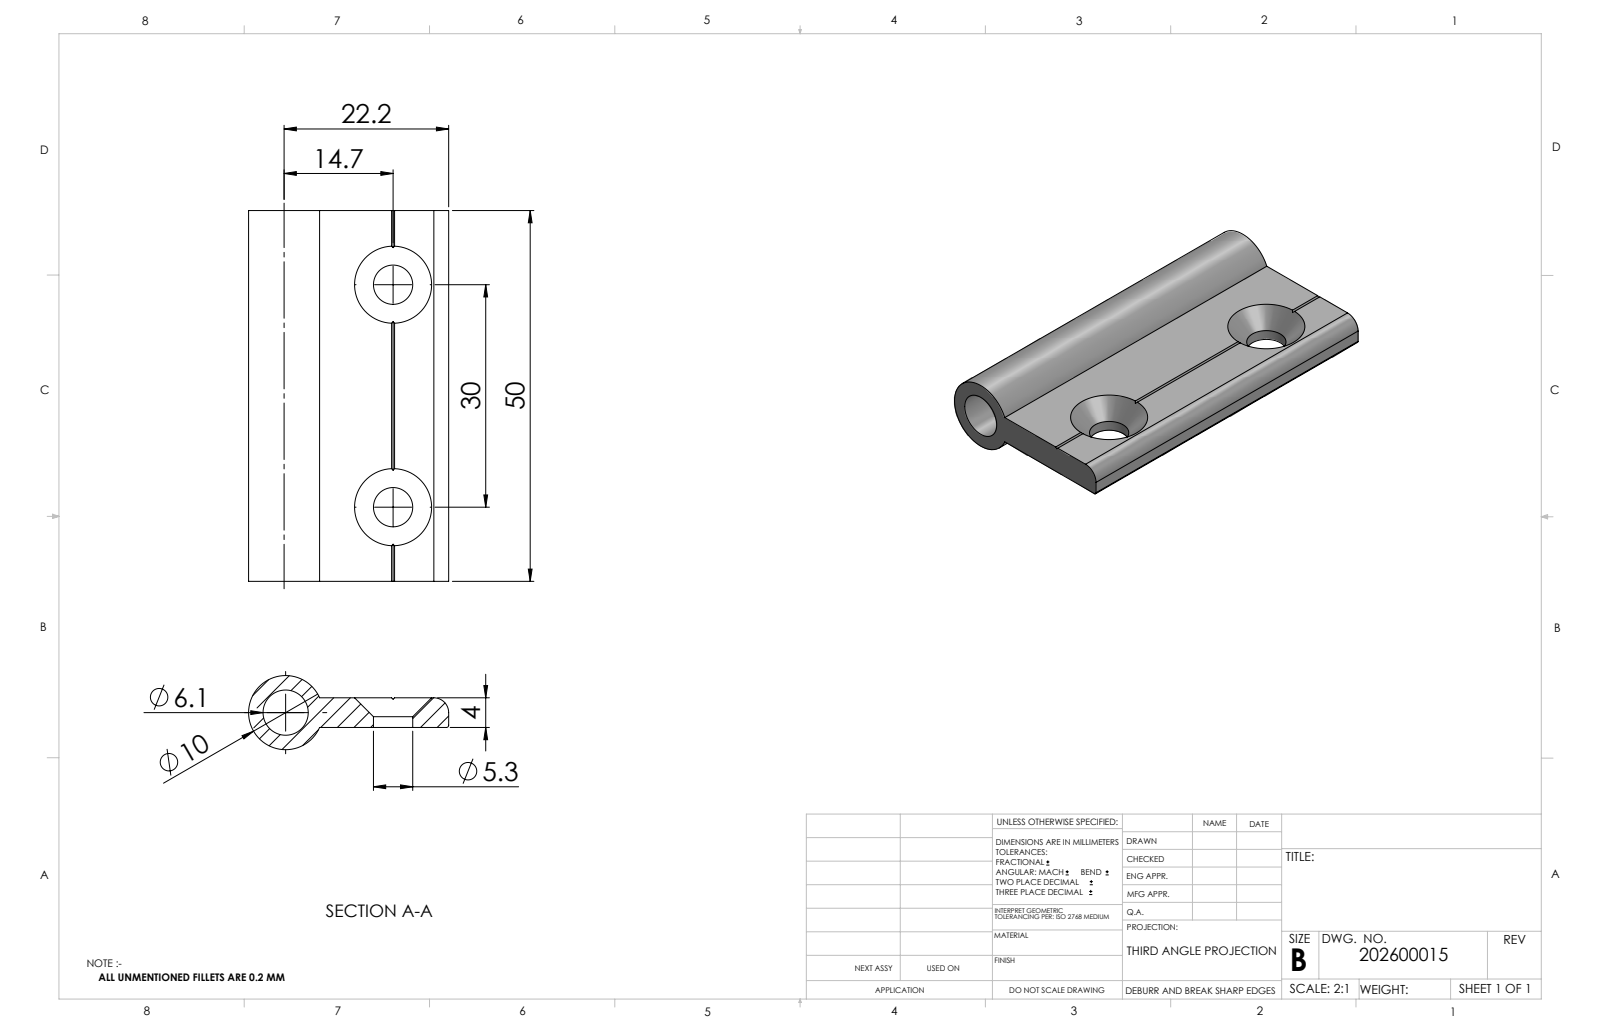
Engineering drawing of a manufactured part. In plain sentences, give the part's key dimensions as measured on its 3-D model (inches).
The part is named "202600015_c_1". Its 3-D file was written by "SolidWorks 2014 (CONFIG_CONTROL_DESIGN)". It is 1 solid with 26 faces: 12 planar, 10 cylindrical and 4 other. Overall it measures 1.969 by 1.063 by 0.394 inches. Its volume is 0.337 cubic inches and its surface area 6.922 square inches. Round holes: 2 of diameter 0.209, 1 of diameter 0.24. Round bosses or shafts: 1 of diameter 0.394. Partial cylindrical surfaces (rounded edges, fillets, slot ends): 1 of radius 0.012, 1 of radius 0.079. The main face-to-face distances are 0.157, 1.969. The hole center spacings are 1.181.
